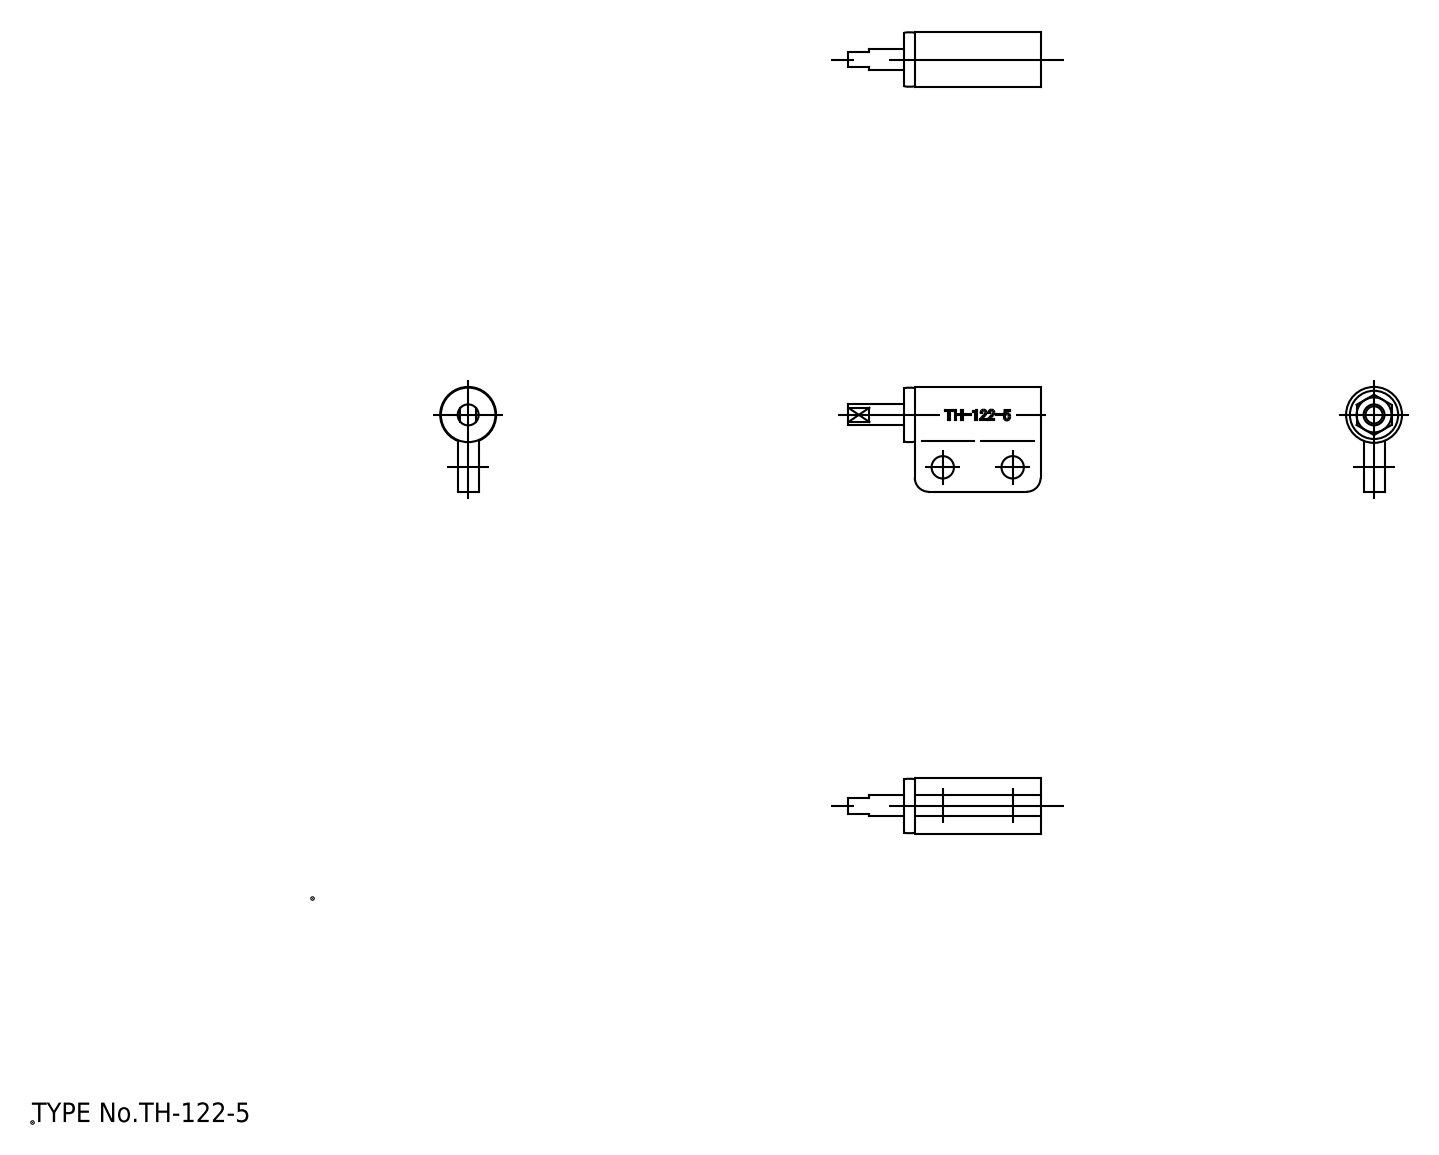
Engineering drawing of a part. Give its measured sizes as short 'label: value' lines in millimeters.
name: PC013-prt0; PC013-prt1; PC013-prt2; PC013-prt3 (+1 more)
written by: spGate 19.8.4 (****-****-****-****) (AUTOMOTIVE_DESIGN)
unit: mm
bodies: 5 solids, 67 faces (25 planar, 24 cylindrical, 18 other)
size: 27.5 × 15 × 8
volume: 1 020 mm³; area: 2 285 mm²
holes: 2× ⌀3.2, 1× ⌀3, 1× ⌀5.77, 1× ⌀6.9
bosses: 1× ⌀8, 1× ⌀6.3
rounds: 2× R2
face distances: 3, 4, 1.5, 15.5, 14, 14.7, 13.2, 0.8, 1, 19.5
hole spacings: 10
